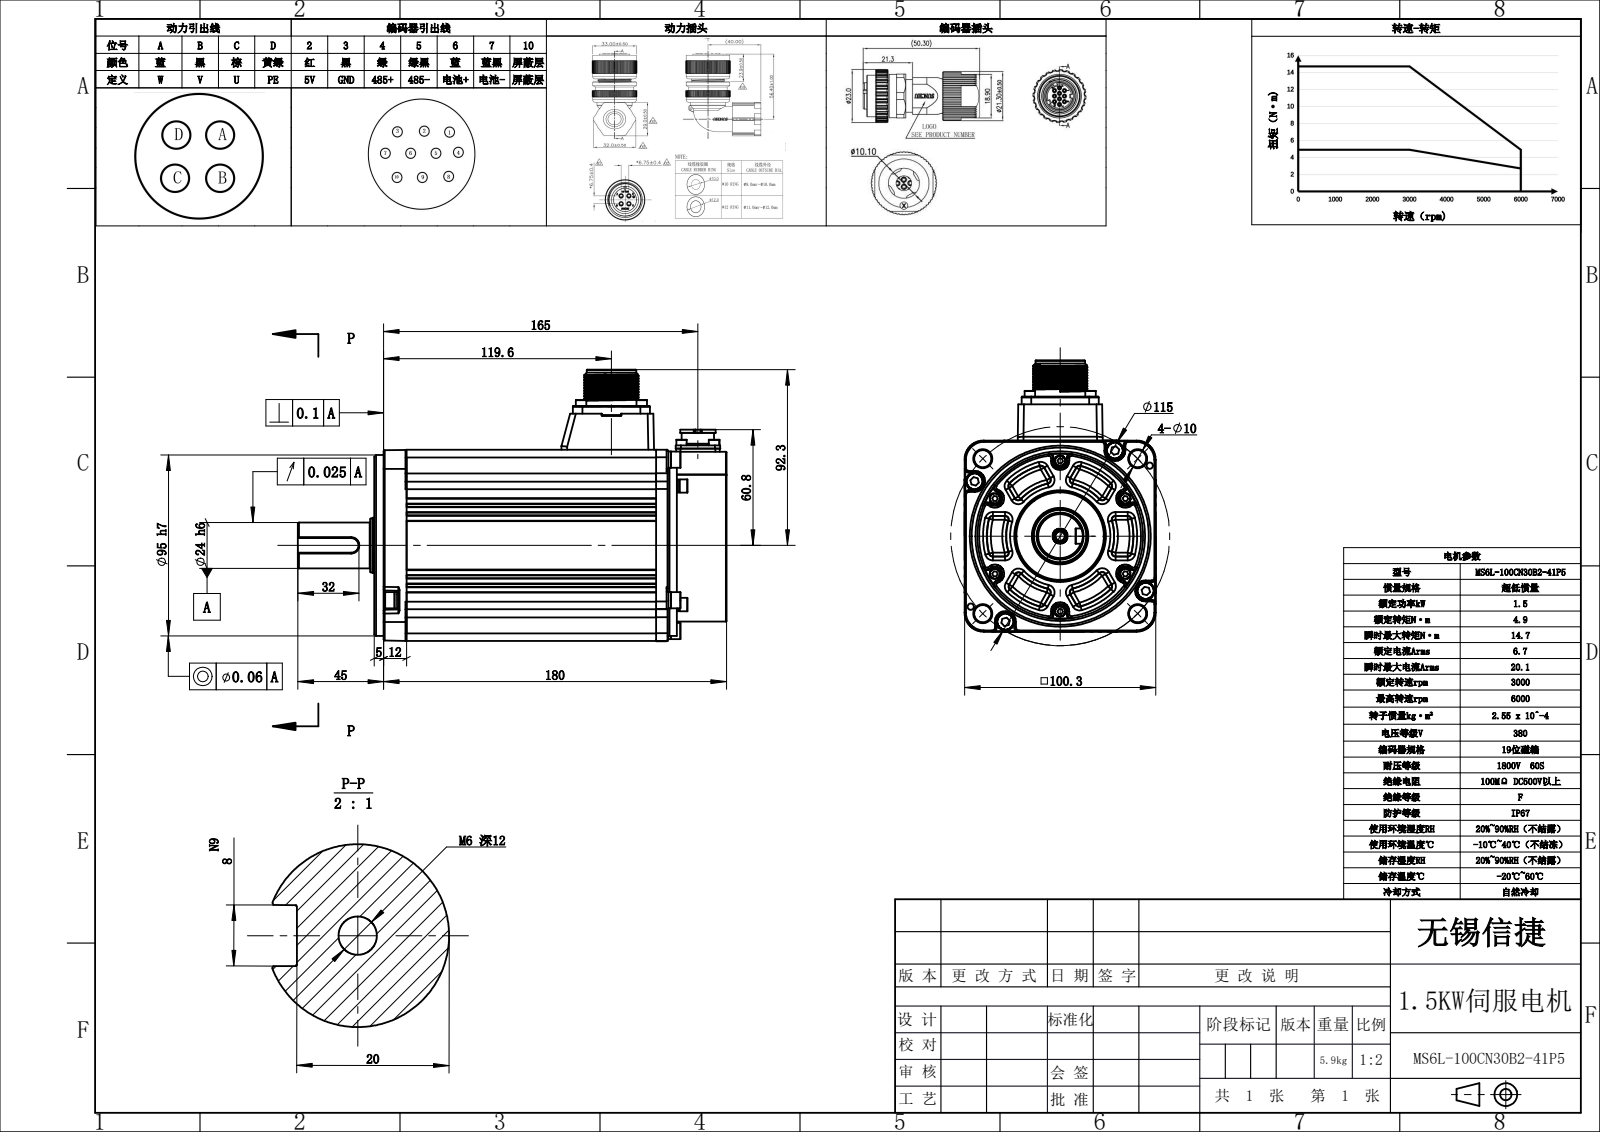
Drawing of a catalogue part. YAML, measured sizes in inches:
part_name: "MS6L-100CN30B2-41P5"
step_written_by: "SolidWorks 2022 (CONFIG_CONTROL_DESIGN)"
units: inches
bodies: {solids: 61, faces: 3307, planar: 1632, cylindrical: 757, other: 918}
overall_size: [8.858, 5.615, 3.967]
volume: 98.68
surface_area: 335.1
round_holes:
  - {diameter: 0.04, count: 10}
  - {diameter: 0.13, count: 10}
  - {diameter: 0.126, count: 8}
  - {diameter: 0.157, count: 8}
  - {diameter: 0.098, count: 6}
  - {diameter: 0.114, count: 4}
  - {diameter: 0.177, count: 4}
  - {diameter: 0.22, count: 4}
  - {diameter: 0.051, count: 1}
  - {diameter: 0.063, count: 1}
  - {diameter: 0.197, count: 1}
  - {diameter: 0.425, count: 1}
round_bosses_or_shafts:
  - {diameter: 0.217, count: 14}
  - {diameter: 0.118, count: 14}
  - {diameter: 0.059, count: 10}
  - {diameter: 0.03, count: 10}
  - {diameter: 0.354, count: 8}
  - {diameter: 0.335, count: 8}
  - {diameter: 0.197, count: 8}
  - {diameter: 0.276, count: 4}
partial_cylinders:
  - {radius: 0.012, count: 65}
  - {radius: 0.079, count: 26}
  - {radius: 0.008, count: 25}
  - {radius: 0.039, count: 21}
  - {radius: 0.157, count: 17}
  - {radius: 0.02, count: 12}
  - {radius: 0.009, count: 8}
  - {radius: 0.091, count: 6}
face_to_face_distances: [5.157, 0.276, 5.433, 5.437, 5.161, 3.949, 3.293, 0.656, 0.039, 1.457]
hole_center_spacings: [0.097, 0.165, 0.904, 0.094, 0.085, 0.127, 0.183, 0.189]
